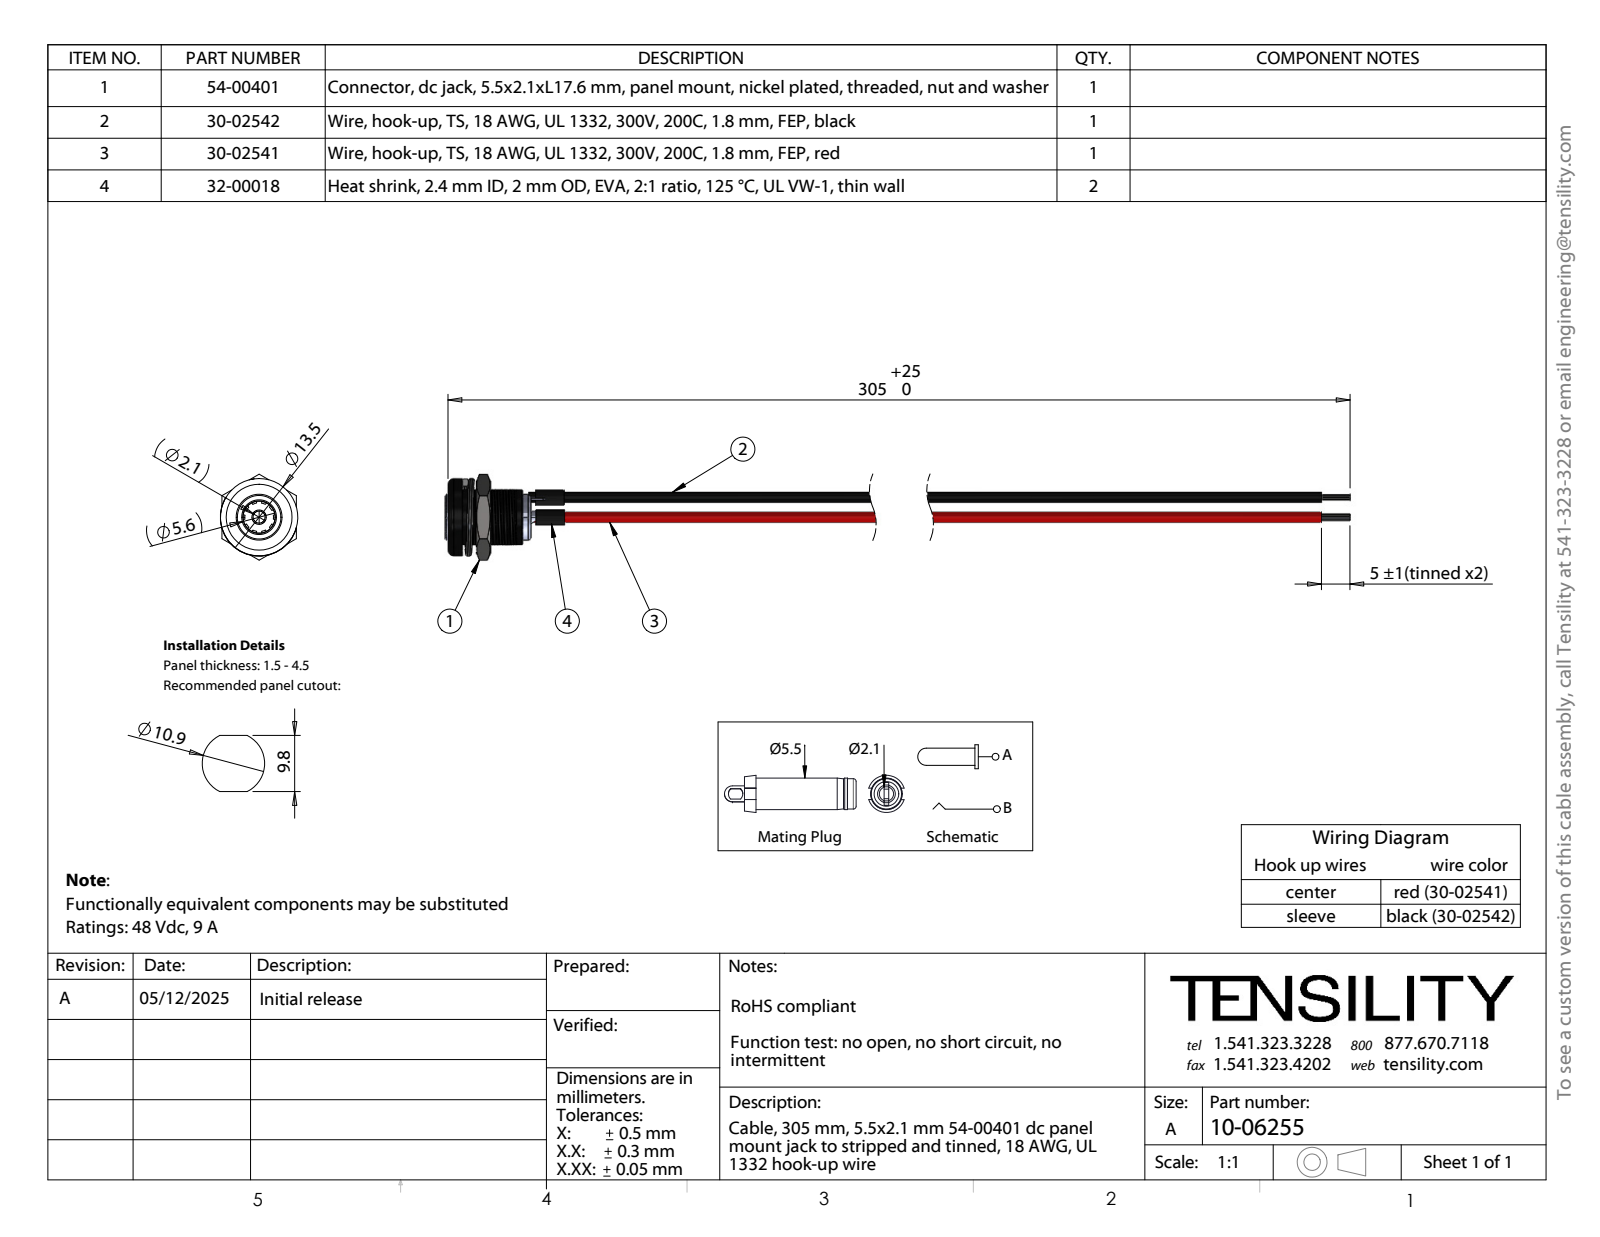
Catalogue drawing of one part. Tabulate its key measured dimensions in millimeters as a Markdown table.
| quantity | value |
| --- | --- |
| part name | 30-02541_stripped and tinned; 32-00018_round 10-06314; 50-01012 shell_Shell; 10-06255 (+8 more) |
| STEP written by | SolidWorks 2021 (CONFIG_CONTROL_DESIGN) |
| units | millimeters |
| bodies | 49 solids, 543 faces (173 planar, 243 cylindrical, 127 other) |
| overall size | 169.59 × 15.01 × 13.55 |
| volume | 1 985 mm³ |
| surface area | 13 358 mm² |
| round holes (diameter × count) | 0.24 × 38, 1.5 × 2, 1.6 × 1, 2.15 × 1, 2.5 × 1, 5.6 × 1, 5.65 × 1, 6.4 × 1, 6.6 × 1, 7.6 × 1, 8 × 1, 10.3 × 1 |
| round bosses / shafts (diameter × count) | 1.8 × 2, 13.5 × 1, 9.6 × 1, 7.3 × 1, 6.2 × 1, 2.1 × 1 |
| partial cylindrical surfaces (radius × count) | 0.5 × 2, 3.35 × 1, 5.4 × 1 |
| main face-to-face distances | 2.5, 4.92, 13, 8.5, 11, 1, 14.1, 11.6, 3.1, 7.42 |
| hole center spacings | 0.65, 0.43, 0.49, 0.42, 0.85, 0.88, 0.89, 0.73 |
